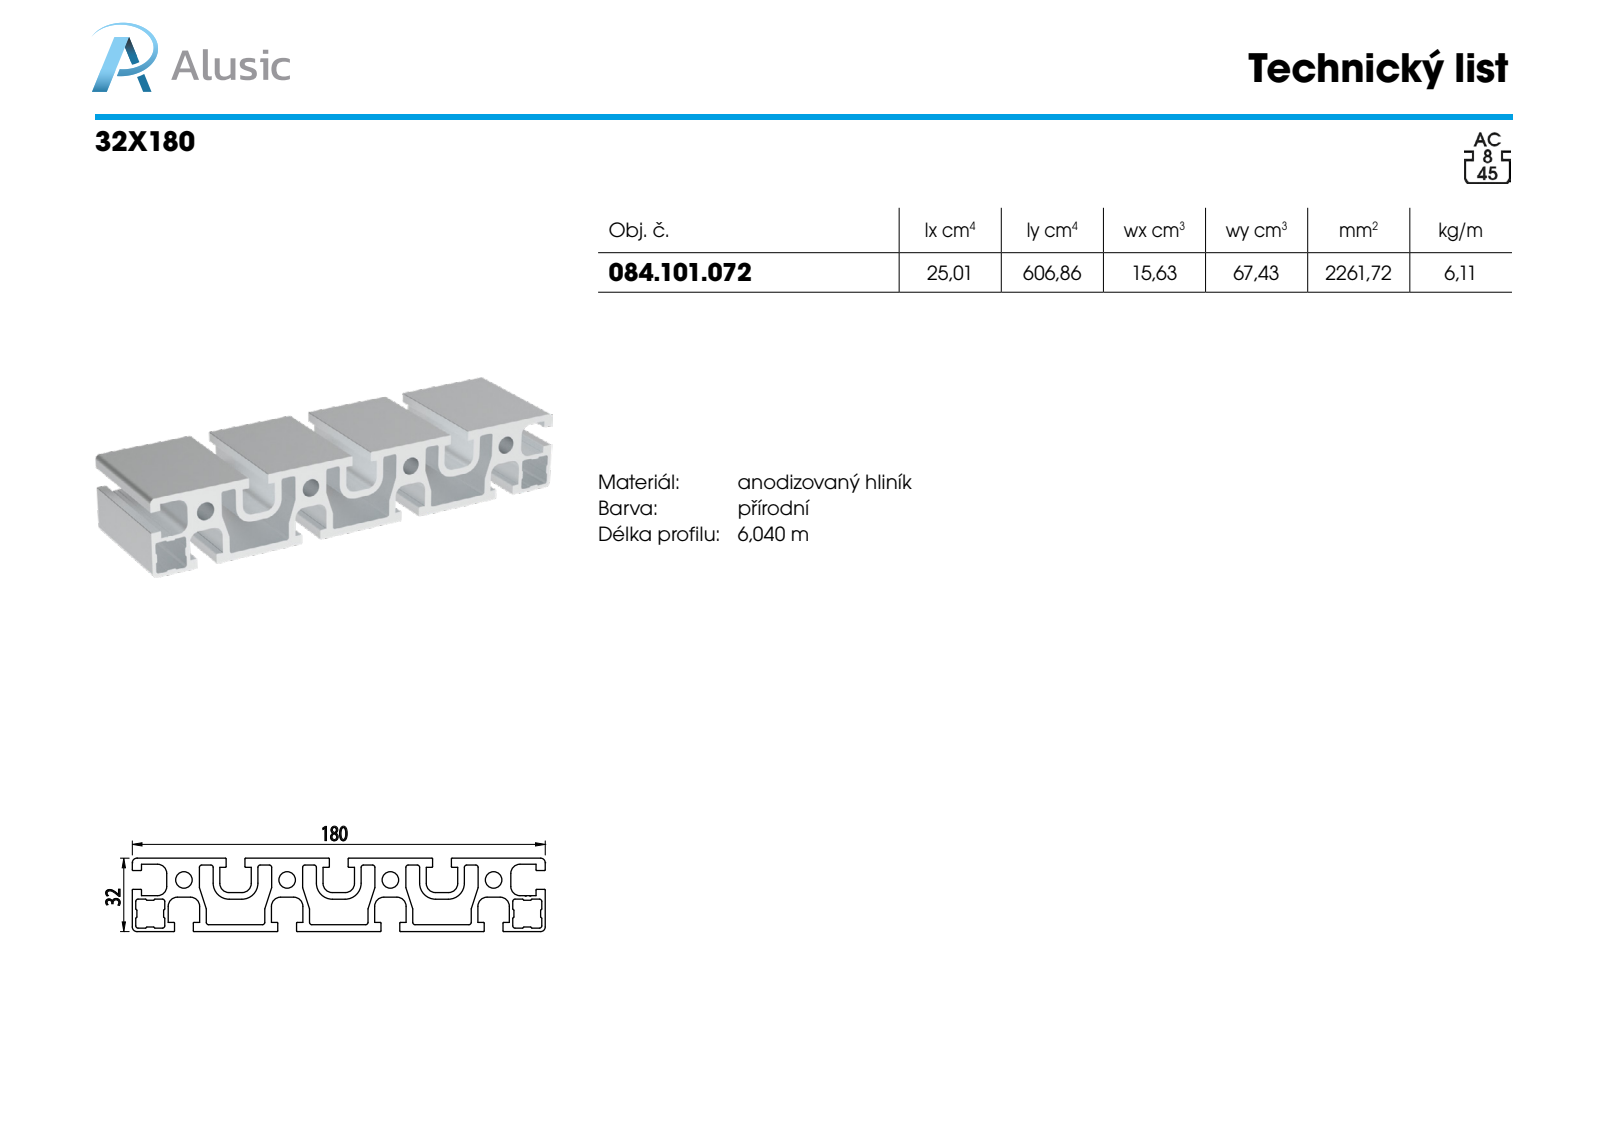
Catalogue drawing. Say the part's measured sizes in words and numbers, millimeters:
The part is named "084.101.072". Its 3-D file was written by "SolidWorks 2018 (AUTOMOTIVE_DESIGN)". It is 1 solid with 260 faces: 156 planar, 104 cylindrical and 0 other. Overall it measures 180 by 100 by 32 millimeters. Its volume is 226 172 cubic millimeters and its surface area 138 460 square millimeters. Round holes: 4 of diameter 7.2. Partial cylindrical surfaces (rounded edges, fillets, slot ends): 36 of radius 0.3, 26 of radius 1, 18 of radius 4, 6 of radius 0.2, 6 of radius 7, 4 of radius 2. The main face-to-face distances are 32, 3, 29, 45, 22.5, 13.7, 15, 90, 31.4, 67.5. The hole center spacings are 45, 90, 135.
